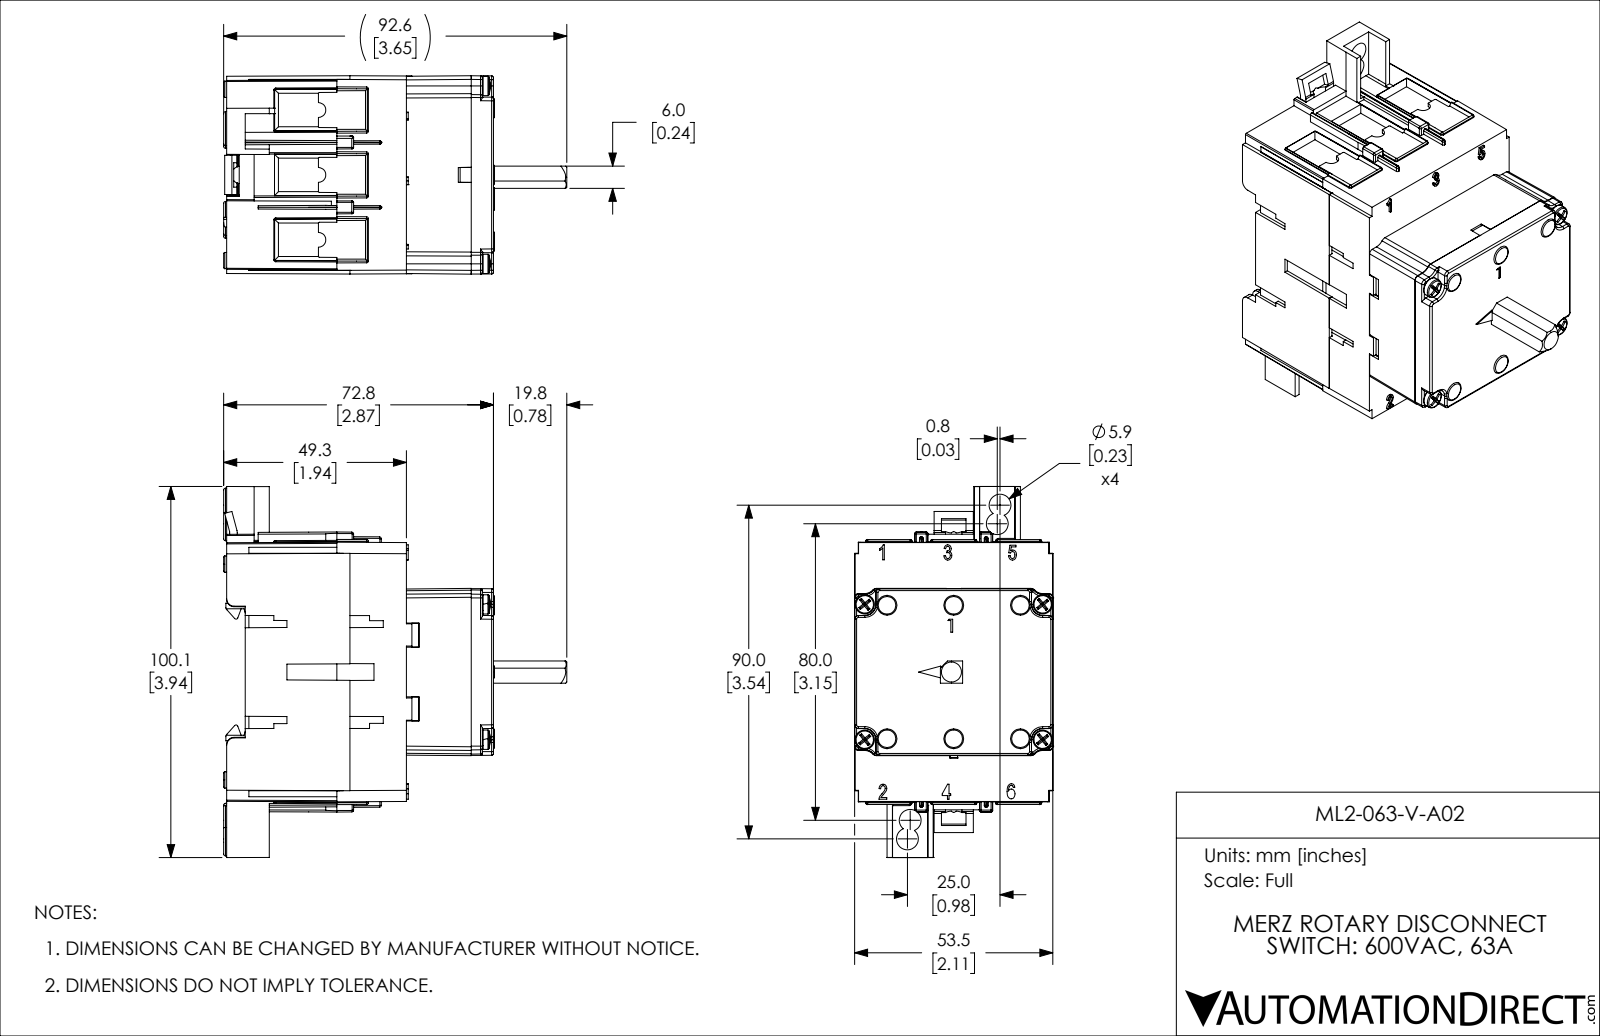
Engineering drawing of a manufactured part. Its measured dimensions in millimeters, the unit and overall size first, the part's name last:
Units: millimetres
Overall size (bounding box): 100.1 × 92.6 × 53.5
Round holes (diameter × count): ⌀5.9 ×4, ⌀4.7 ×1, ⌀32.9 ×1
Round bosses / shafts (diameter × count): ⌀5.2 ×4
Partial cylindrical surfaces — rounded edges, fillets, slot ends (radius × count): R0.5 ×60, R0.4 ×32, R0.3 ×26, R1 ×18, R2 ×9, R1.5 ×2
Main face-to-face distances: 1, 67, 5, 39.5, 6, 60, 27.5, 40.2, 0.7, 26.8
Hole centre spacings: 5.1, 41.7, 46.7, 88.4, 83.4, 93.4
Volume: 217 800 mm³ · Surface area: 44 370 mm²
Bodies: 1 solid, 1576 faces (1029 planar, 249 cylindrical, 298 other)
Part name (STEP PRODUCT): ML2-063-V-A02
STEP written by: SolidWorks 2019 (AUTOMOTIVE_DESIGN)
